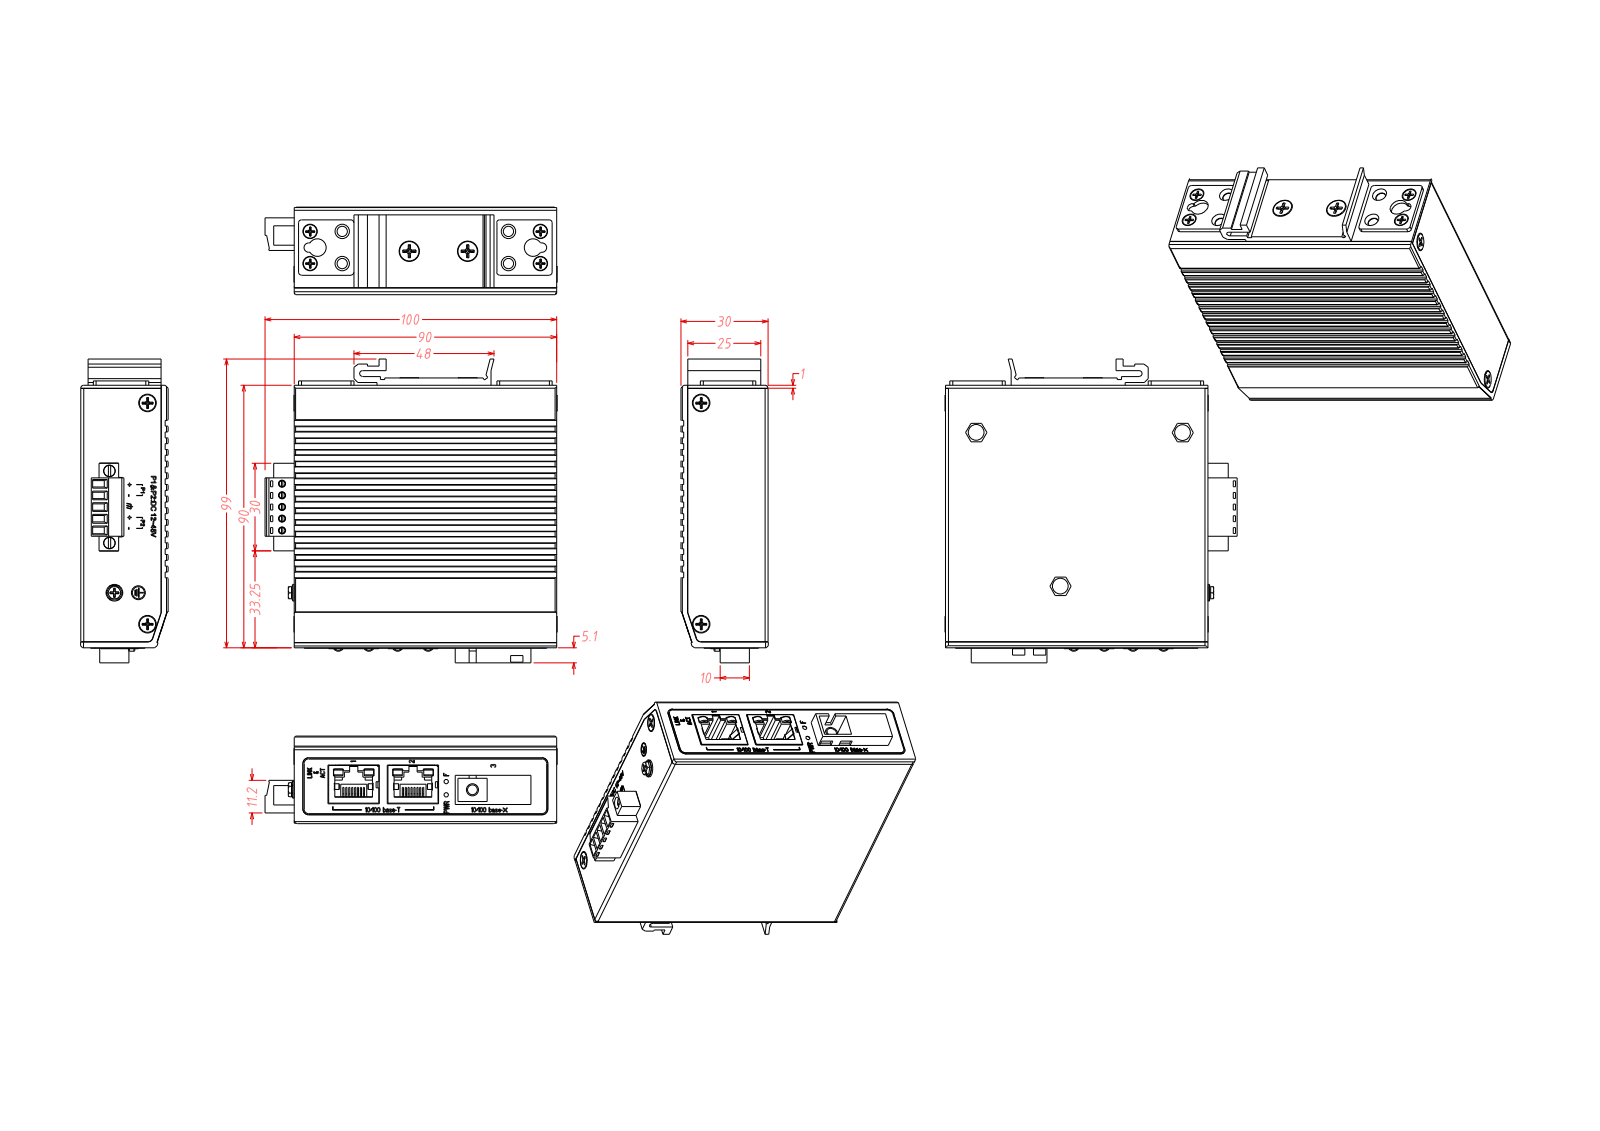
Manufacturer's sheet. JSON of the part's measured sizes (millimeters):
{"part_name": "BODY_32; BODY_31; BODY_30; BODY_29 (+8 more)", "step_written_by": "PRO/ENGINEER BY PARAMETRIC TECHNOLOGY CORPORATION, 2011310 (CONFIG_CONTROL_DESIGN)", "units": "millimeters", "bodies": {"solids": 33, "faces": 3394, "planar": 2895, "cylindrical": 345, "other": 154}, "overall_size": [104.1, 100.15, 30], "volume_mm3": 72974, "surface_area_mm2": 89314, "round_holes": [[2.5, 12], [3.5, 8], [2.4, 5], [4, 4], [4.2, 3], [5.4, 3], [1.44, 2], [2.2, 2], [3.6, 2], [6, 2], [1.95, 1], [3.4, 1]], "round_bosses_or_shafts": [[3.7, 7], [2.16, 5], [2.05, 5], [1, 5], [0.2, 5], [2.39, 4], [3.8, 2], [3.43, 2]], "partial_cylinders_radius": [[0.2, 36], [1, 27], [2, 8], [0.38, 6], [1.58, 4], [1.89, 4], [1.98, 4], [1.6, 3]], "face_to_face_distances": [1, 5, 21.4, 4, 28.9, 26.4, 25.4, 5.6, 1.6, 6.6], "hole_center_spacings": [11, 4, 6.04, 10.12, 15.56, 65.73, 68, 68.88]}
